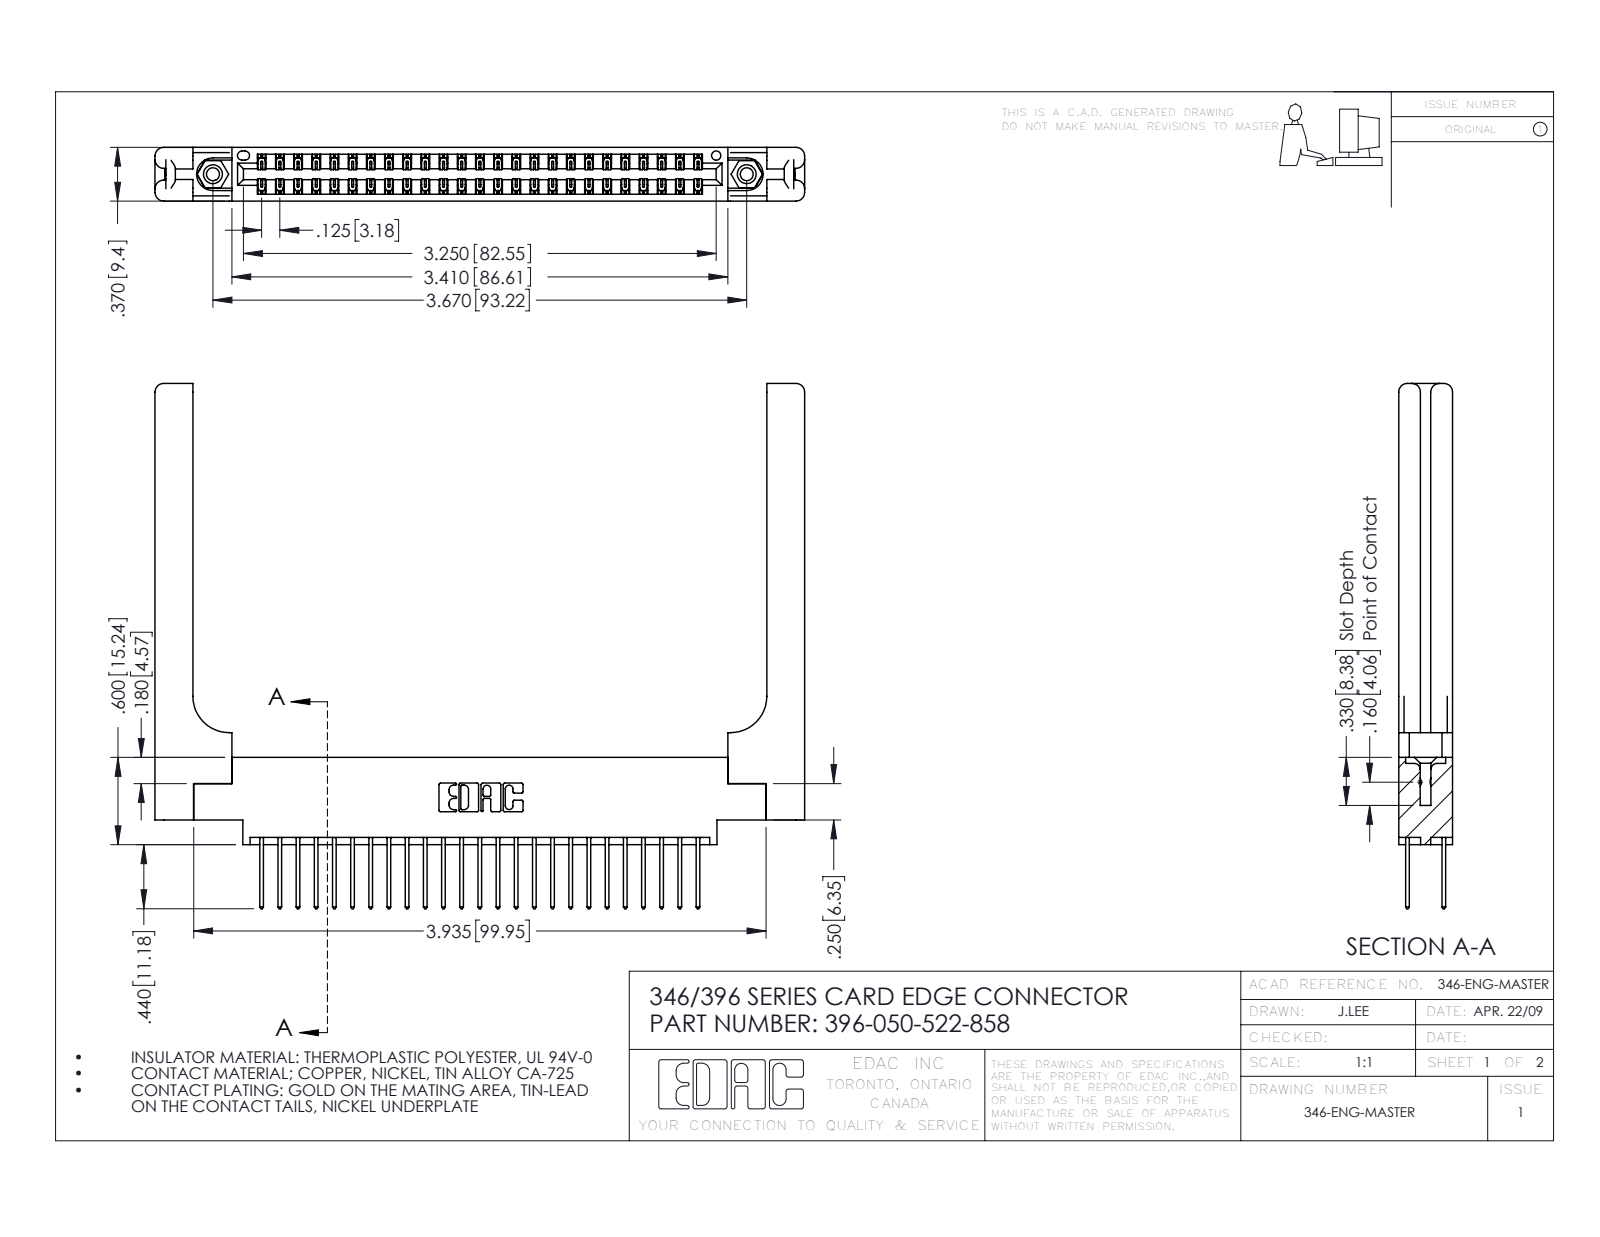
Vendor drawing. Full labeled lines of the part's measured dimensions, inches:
Part name (STEP PRODUCT): 345-292-001_345-293-122; 396-050-522-858; 346-220-058_345-220-058; 345-250-001_345-250-001-102 (+1 more)
STEP written by: SolidWorks 2016 (CONFIG_CONTROL_DESIGN)
Units: inches
Bodies: 55 solids, 2982 faces (1978 planar, 944 cylindrical, 60 other)
Overall size (bounding box): 4.466 × 3.61 × 0.37
Volume: 1.123 in³ · Surface area: 31.72 in²
Round holes (diameter × count): ⌀0.089 ×2, ⌀0.125 ×2, ⌀0.156 ×2, ⌀0.064 ×1
Round bosses / shafts (diameter × count): ⌀0.155 ×2
Partial cylindrical surfaces — rounded edges, fillets, slot ends (radius × count): R0.006 ×75, R0.01 ×50, R0.01 ×22, R0.06 ×16, R0.007 ×6, R0.031 ×6, R0.026 ×3, R0.014 ×2
Main face-to-face distances: 0.37, 0.072, 0.048, 0.322, 0.25, 0.148, 0.15, 0.025, 0.298, 0.275
Hole centre spacings: 0.246, 3.462, 3.67
